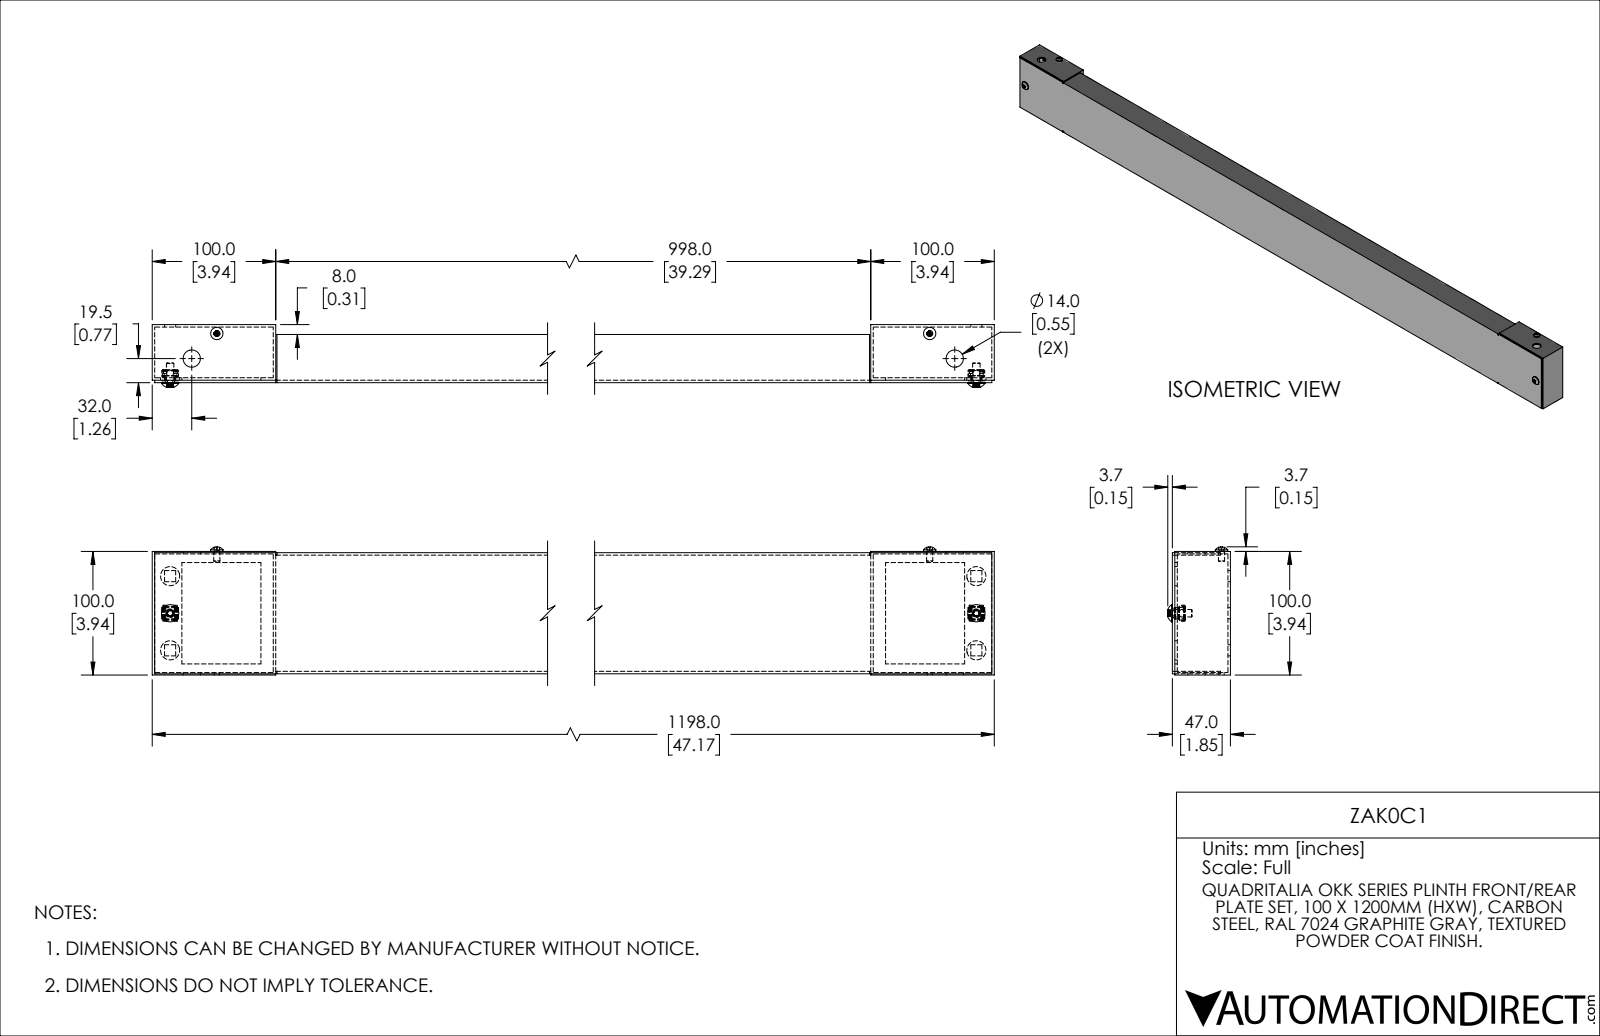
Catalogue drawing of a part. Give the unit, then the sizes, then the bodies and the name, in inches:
Units: inches
Overall size (bounding box): 47.165 × 4.084 × 1.996
Round holes (diameter × count): ⌀0.61 ×4, ⌀0.167 ×2, ⌀0.194 ×2, ⌀0.276 ×2, ⌀0.551 ×2
Round bosses / shafts (diameter × count): ⌀0.551 ×2, ⌀0.394 ×2, ⌀0.236 ×2, ⌀0.197 ×2
Partial cylindrical surfaces — rounded edges, fillets, slot ends (radius × count): R0.02 ×42, R0.01 ×28, R0.039 ×18
Main face-to-face distances: 0.079, 3.78, 3.858, 0.039, 1.772, 3.701, 3.819, 1.693, 1.85, 0.118
Hole centre spacings: 1.181, 46.039, 46.024, 1.13, 2.362, 43.854, 46.084, 43.047
Volume: 30.75 in³ · Surface area: 795.6 in²
Bodies: 11 solids, 402 faces (254 planar, 130 cylindrical, 18 other)
Part name (STEP PRODUCT): ZAK0C1
STEP written by: SolidWorks 2021 (CONFIG_CONTROL_DESIGN)
